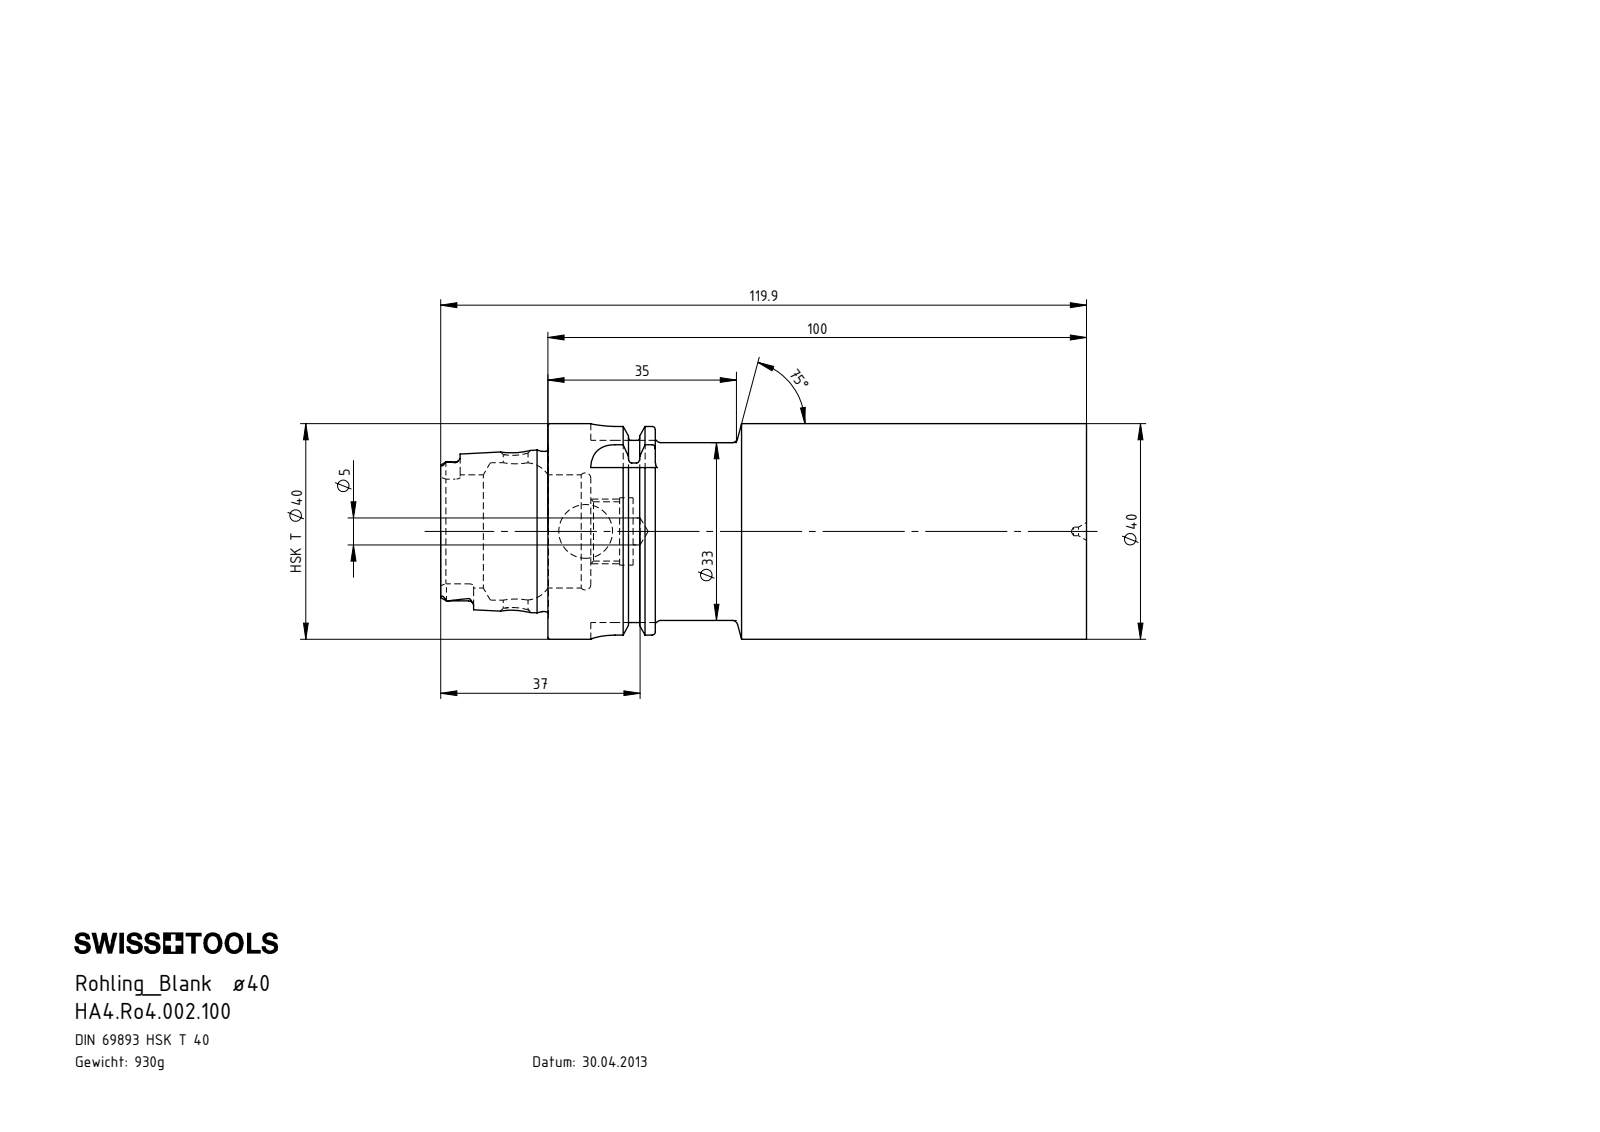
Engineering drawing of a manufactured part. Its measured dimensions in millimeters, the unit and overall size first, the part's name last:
Units: millimetres
Overall size (bounding box): 123.9 × 40 × 40
Round holes (diameter × count): ⌀1.6 ×1, ⌀4.6 ×1, ⌀5 ×1, ⌀10 ×1, ⌀11 ×1, ⌀12.5 ×1, ⌀21 ×1, ⌀25.5 ×1
Round bosses / shafts (diameter × count): ⌀40 ×1, ⌀34.75 ×1, ⌀33 ×1, ⌀29.71 ×1, ⌀6 ×1
Partial cylindrical surfaces — rounded edges, fillets, slot ends (radius × count): R0.9 ×6, R1.88 ×4, R4.5 ×4
Main face-to-face distances: 100, 7.95, 92.05, 19.95, 12, 80.05, 19.9, 27.85, 39.85, 119.9
Volume: 118 600 mm³ · Surface area: 20 003 mm²
Bodies: 1 solid, 129 faces (47 planar, 35 cylindrical, 47 other)
Part name (STEP PRODUCT): HA4.Ro4.002.100
STEP written by: SolidWorks 2017 (CONFIG_CONTROL_DESIGN)
